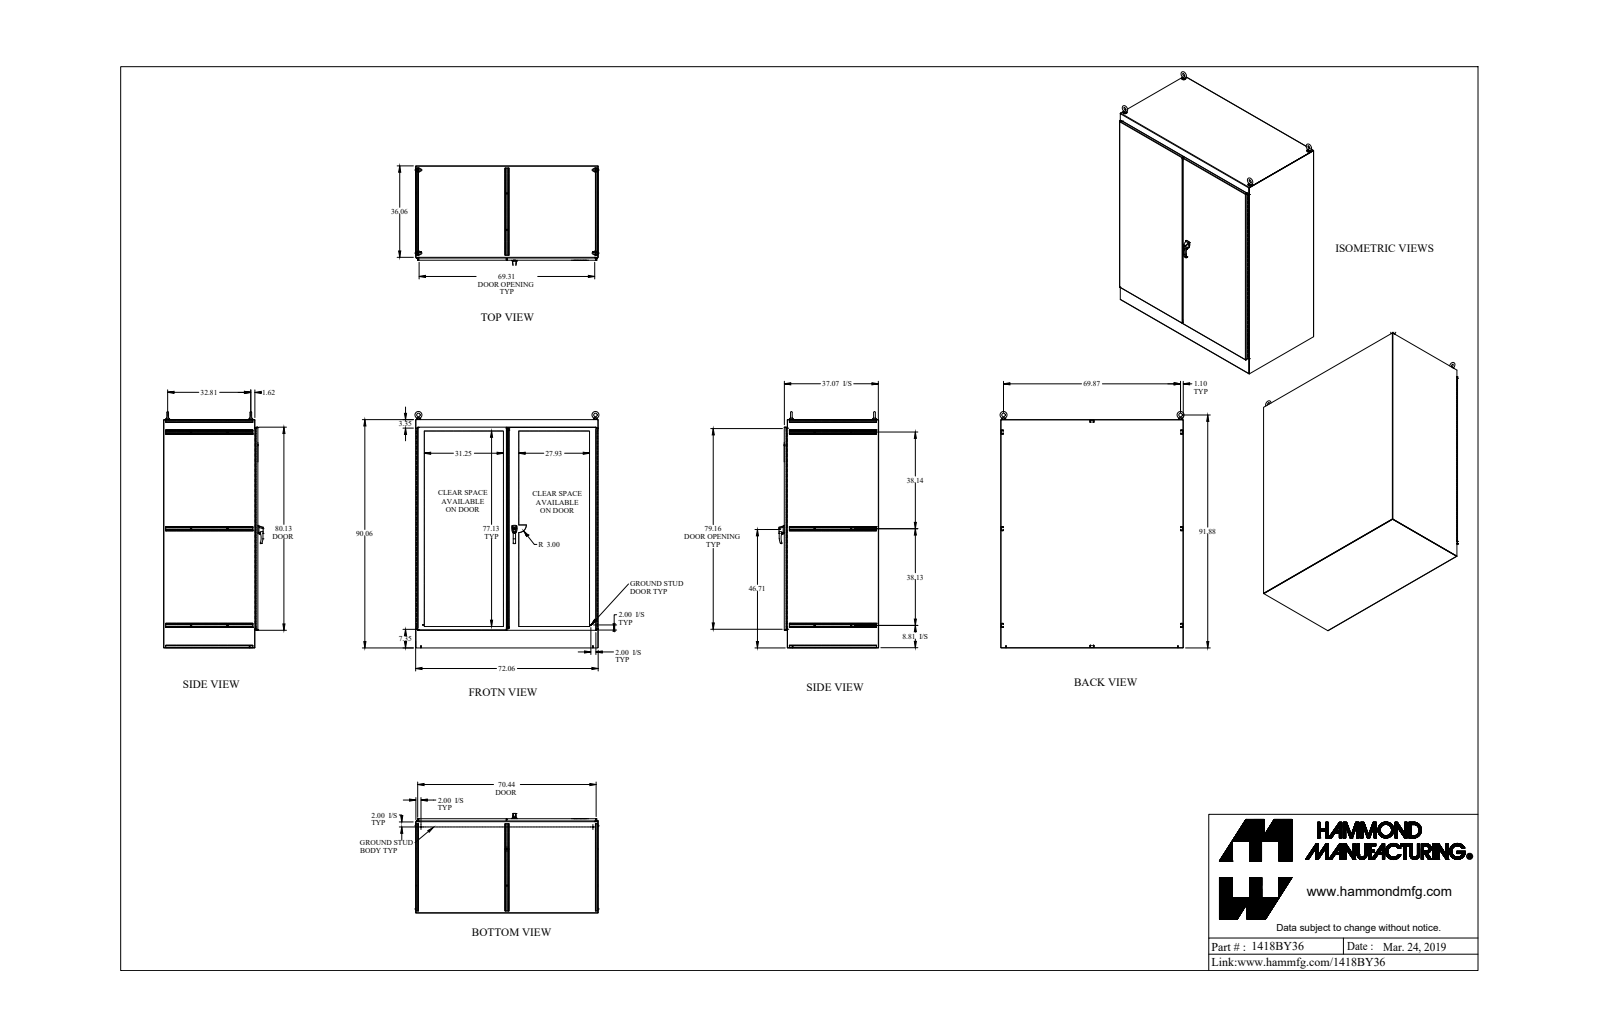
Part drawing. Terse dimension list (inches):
name: 1418BY36
written by: SolidWorks 2019 (AUTOMOTIVE_DESIGN)
unit: in
bodies: 80 solids, 3370 faces (1915 planar, 1280 cylindrical, 175 other)
size: 93.713 × 73.118 × 39.337
volume: 2 803 in³; area: 57 489 in²
holes: 28× ⌀0.304, 14× ⌀0.5, 7× ⌀0.35, 4× ⌀0.527, 4× ⌀0.625, 4× ⌀0.687, 4× ⌀0.75, 2× ⌀0.11, 2× ⌀0.25, 2× ⌀0.257, 2× ⌀0.28, 2× ⌀0.281
bosses: 6× ⌀0.281, 4× ⌀1.75, 4× ⌀1.5, 4× ⌀1.25, 4× ⌀0.738, 4× ⌀0.25, 2× ⌀1, 2× ⌀0.75
rounds: 54× R0.043, 48× R0.138, 25× R0.5, 22× R0.125, 16× R0.018, 15× R0.06, 8× R0.048, 8× R0.05
face distances: 0.095, 0.125, 71.965, 0.072, 37.096, 37.222, 37.024, 37.15, 89.965, 71.87
hole spacings: 6, 70.584, 12, 71.345, 18, 72.595, 24, 74.311
